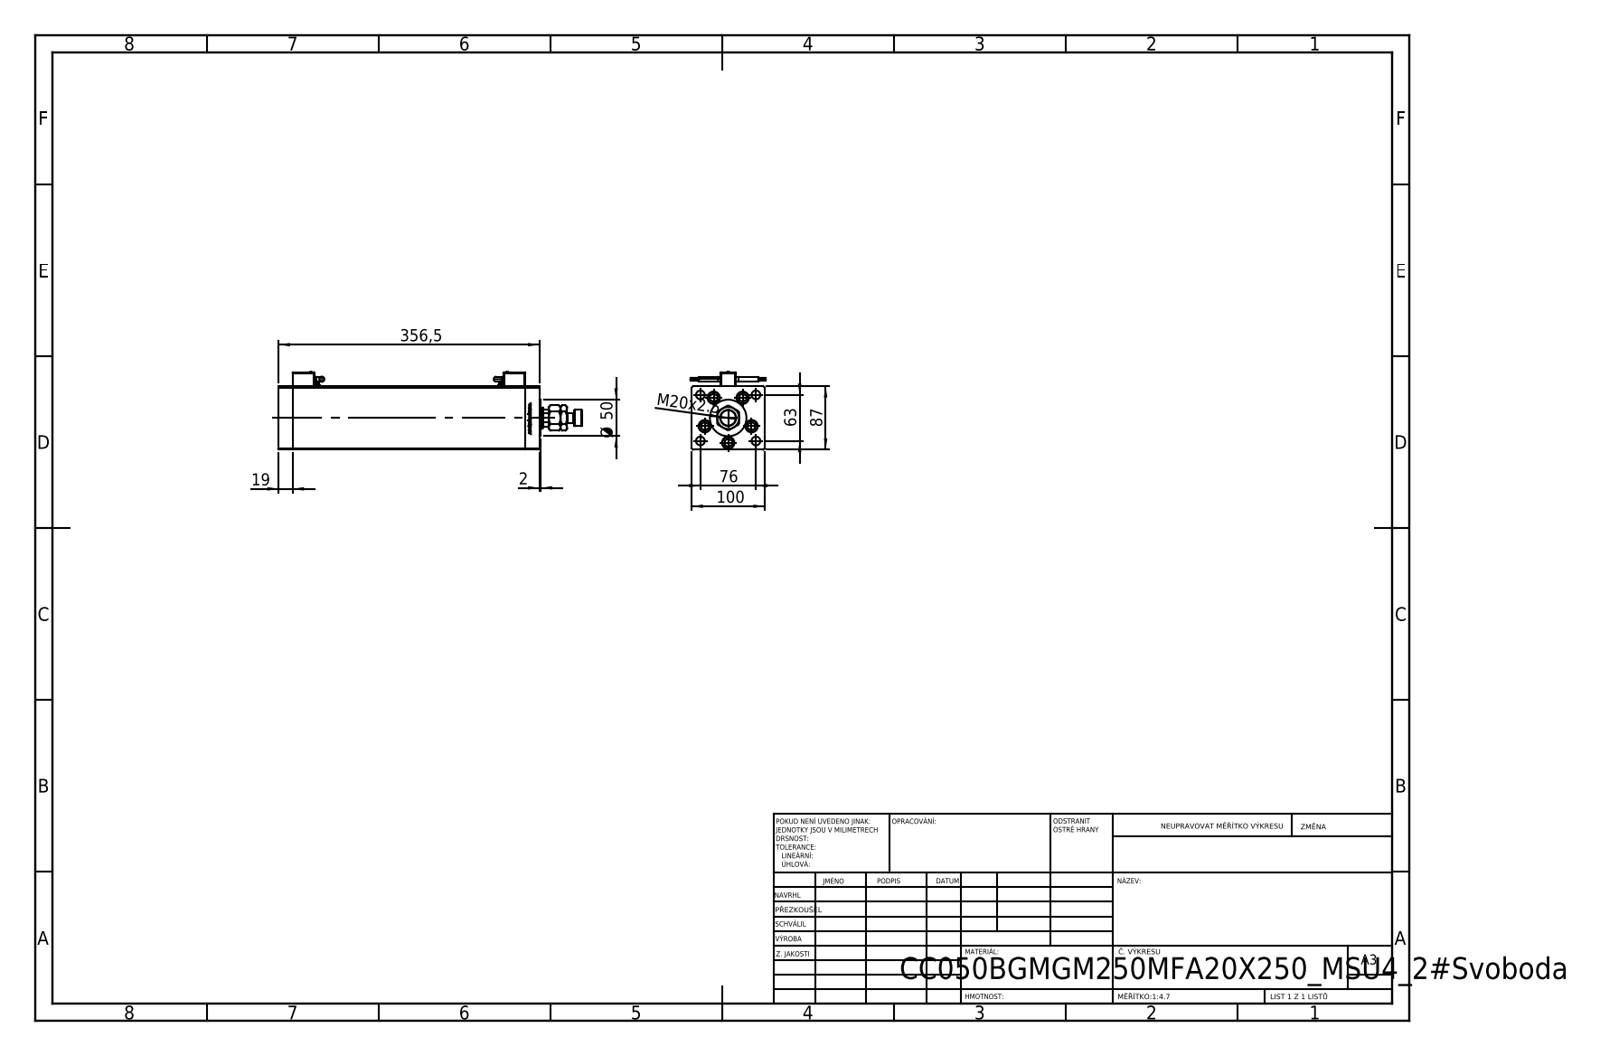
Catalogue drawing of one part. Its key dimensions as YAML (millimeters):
part_name: "V220C_FRONT_B; ALLEN BOLT; V220C_B MIDDLE; V220C_VC_B (+3 more)"
step_written_by: "SolidWorks 2019 (CONFIG_CONTROL_DESIGN)"
units: millimeters
bodies: {solids: 17, faces: 1439, planar: 556, cylindrical: 241, other: 642}
overall_size: [414.5, 107.1, 101.6]
volume: 2710000
surface_area: 330880
round_holes:
  - {diameter: 13.5, count: 7}
  - {diameter: 17, count: 5}
  - {diameter: 12, count: 4}
  - {diameter: 2, count: 2}
  - {diameter: 3.6, count: 2}
  - {diameter: 5, count: 2}
  - {diameter: 7, count: 2}
  - {diameter: 13.16, count: 2}
  - {diameter: 18.5, count: 1}
  - {diameter: 28, count: 1}
round_bosses_or_shafts:
  - {diameter: 0.85, count: 8}
  - {diameter: 8, count: 5}
  - {diameter: 7, count: 4}
  - {diameter: 17, count: 2}
  - {diameter: 6, count: 2}
  - {diameter: 3.5, count: 2}
  - {diameter: 2.5, count: 2}
  - {diameter: 50, count: 1}
partial_cylinders:
  - {radius: 1, count: 24}
  - {radius: 4, count: 4}
  - {radius: 0.93, count: 2}
  - {radius: 13.5, count: 1}
face_to_face_distances: [100, 87, 19, 318.5, 337.5, 34.25, 356.5, 10.5, 76.5, 80.5]
hole_center_spacings: [34, 18.59, 39.64, 49.36, 57.95, 8.25, 21.03, 38.08]
